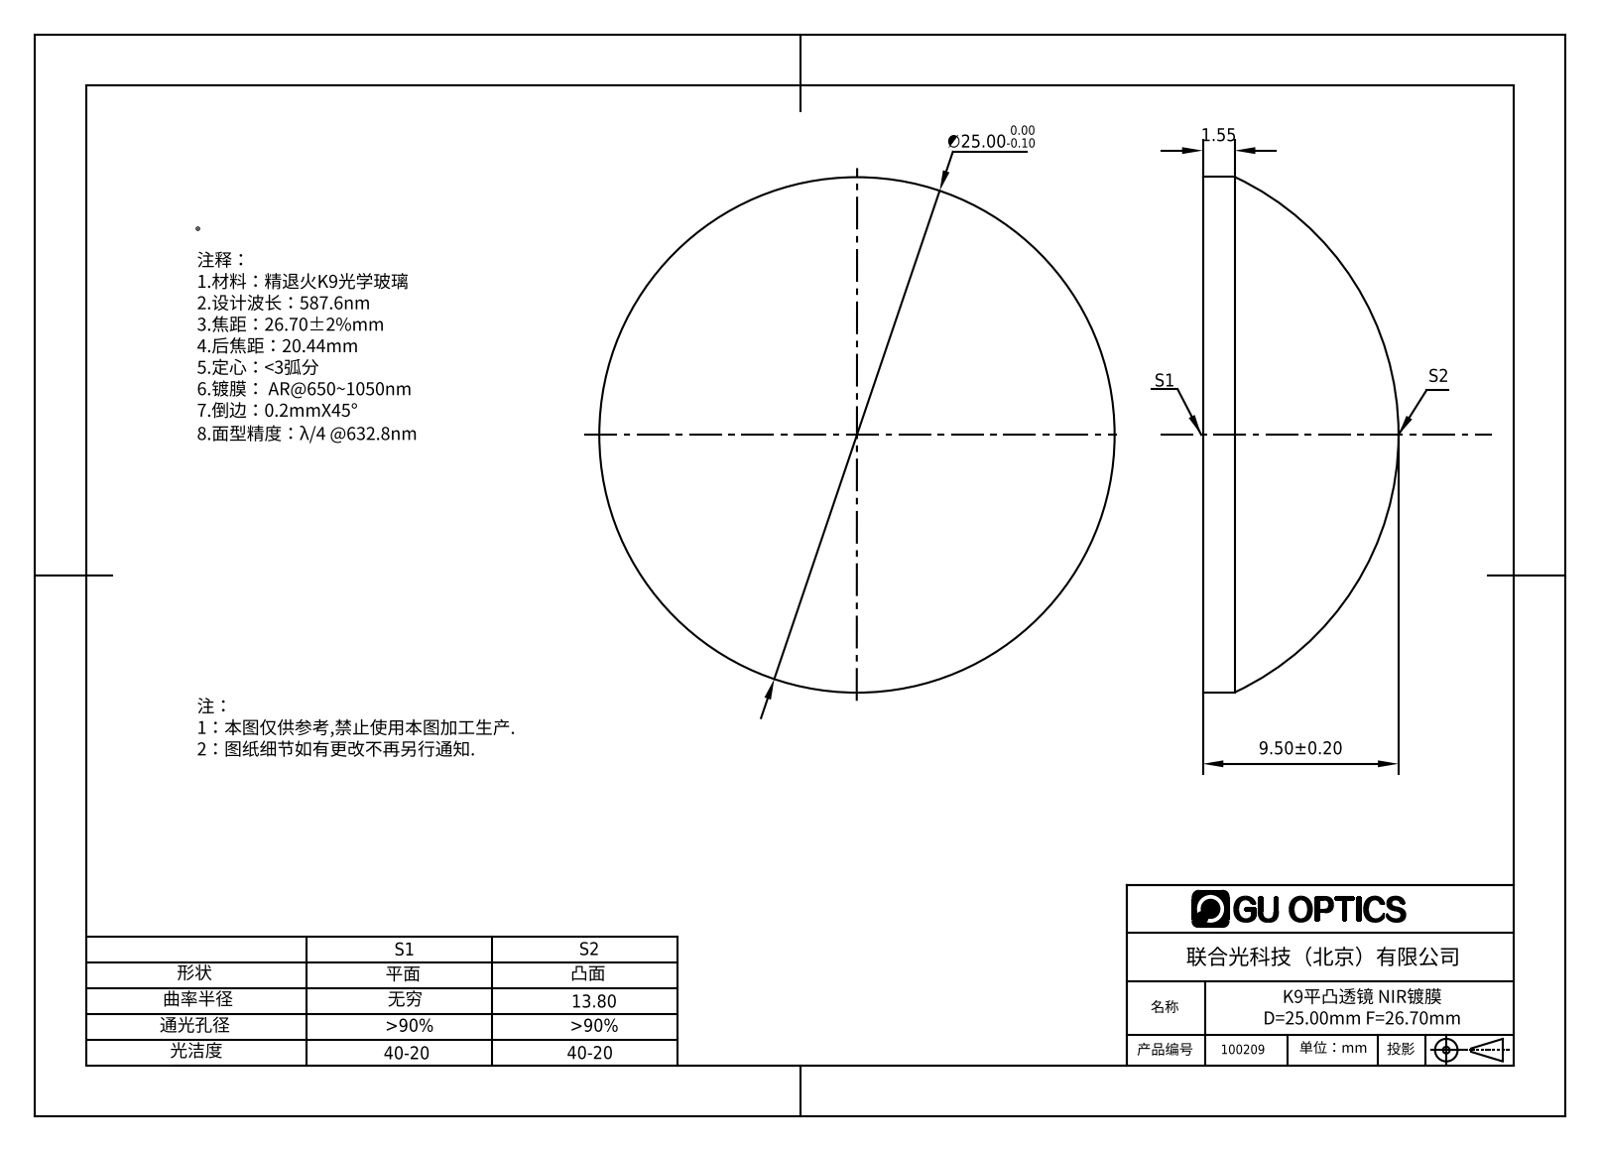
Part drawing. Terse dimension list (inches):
name: 100209
written by: SolidWorks 2016 (AUTOMOTIVE_DESIGN)
unit: in
bodies: 1 solid, 5 faces (1 planar, 2 cylindrical, 2 other)
size: 0.984 × 0.984 × 0.374
volume: 0.182 in³; area: 2.018 in²
bosses: 1× ⌀0.984
